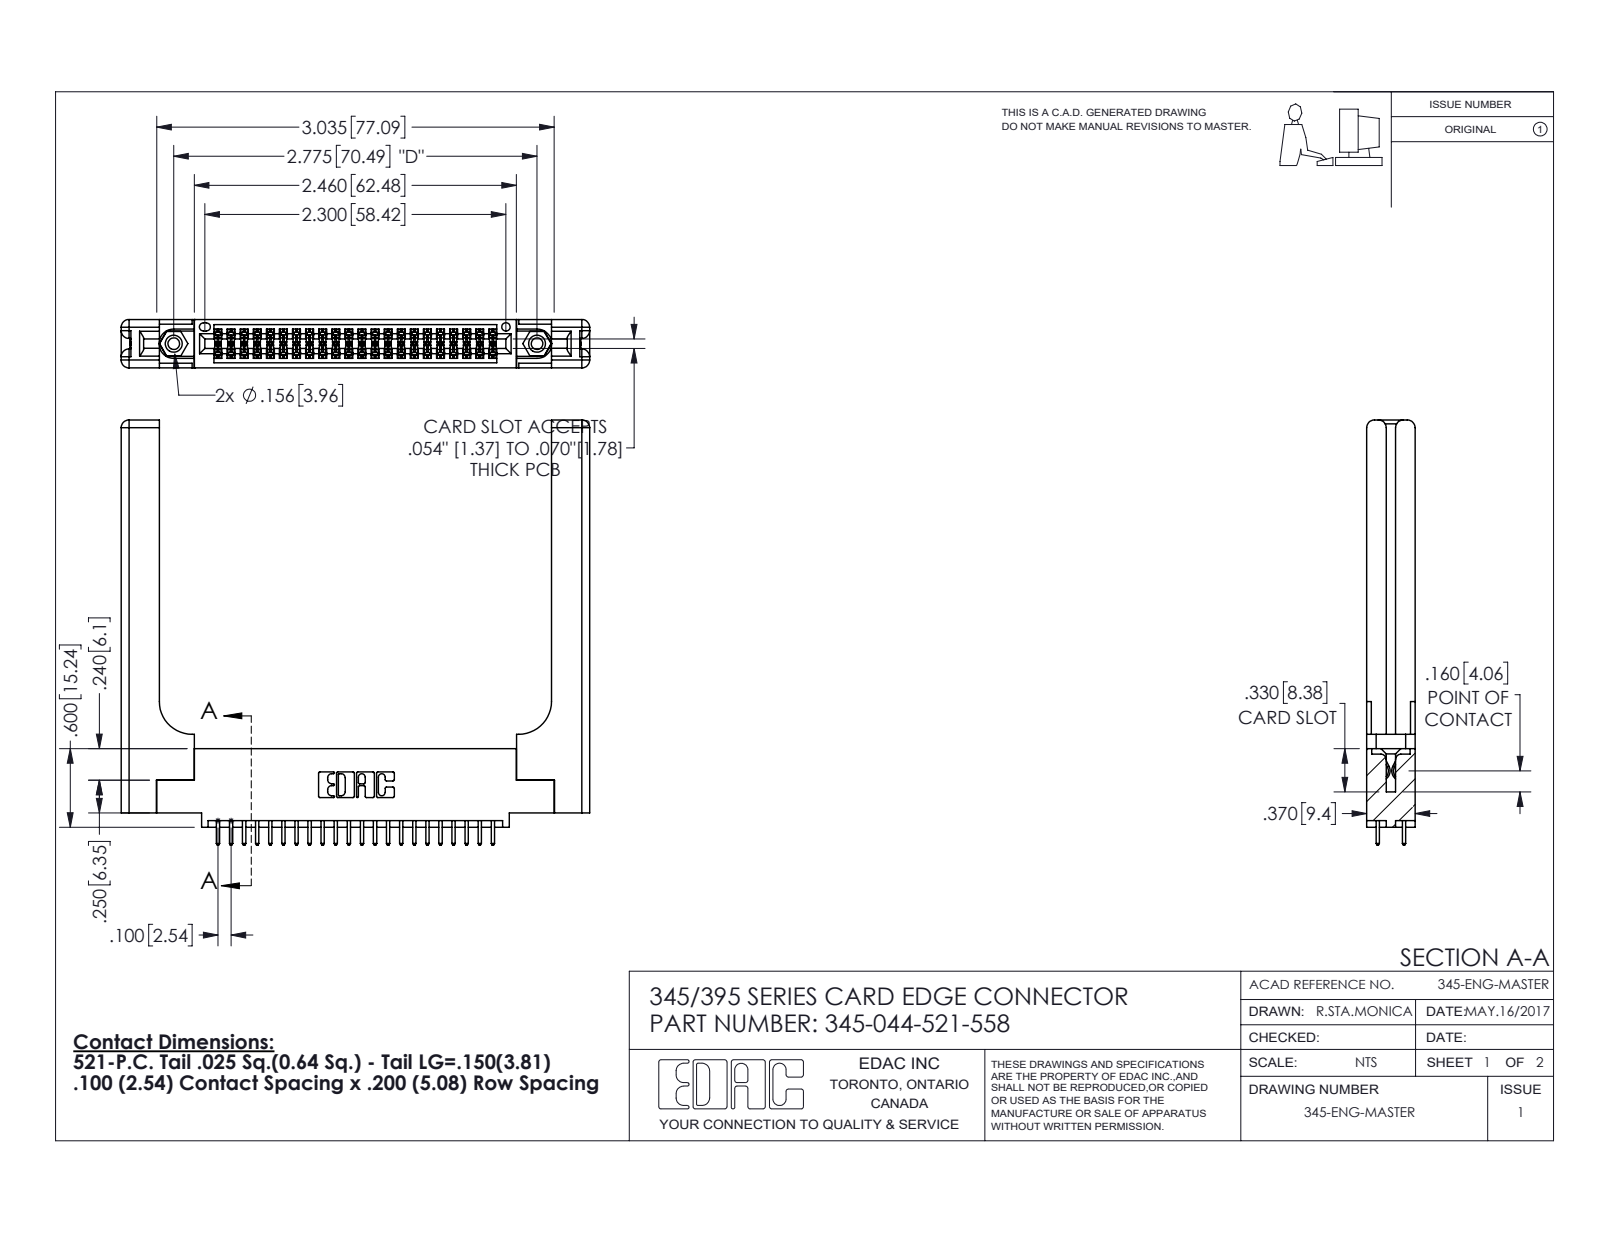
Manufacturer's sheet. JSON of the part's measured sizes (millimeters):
{"part_name": "345-250-001_345-250-001-102; 345-292-001_345-293-121; 345-220-058_345-220-058; 345-044-521-558 (+1 more)", "step_written_by": "SolidWorks 2016 (CONFIG_CONTROL_DESIGN)", "units": "millimeters", "bodies": {"solids": 49, "faces": 2586, "planar": 1684, "cylindrical": 842, "other": 60}, "overall_size": [90.9, 82.5, 9.4], "volume_mm3": 17030, "surface_area_mm2": 17290, "round_holes": [[2.3, 2], [3.2, 2], [4, 2], [1.6, 1]], "round_bosses_or_shafts": [[3.9, 2]], "partial_cylinders_radius": [[0.2, 66], [0.3, 44], [0.3, 22], [1.5, 16], [0.2, 6], [0.8, 6], [0.7, 3], [0.4, 2]], "face_to_face_distances": [9.4, 1.8, 7.6, 3.8, 3.8, 2.5, 6.9, 0.6, 5.1, 5.7], "hole_center_spacings": [6.9, 64.5, 70.5]}
